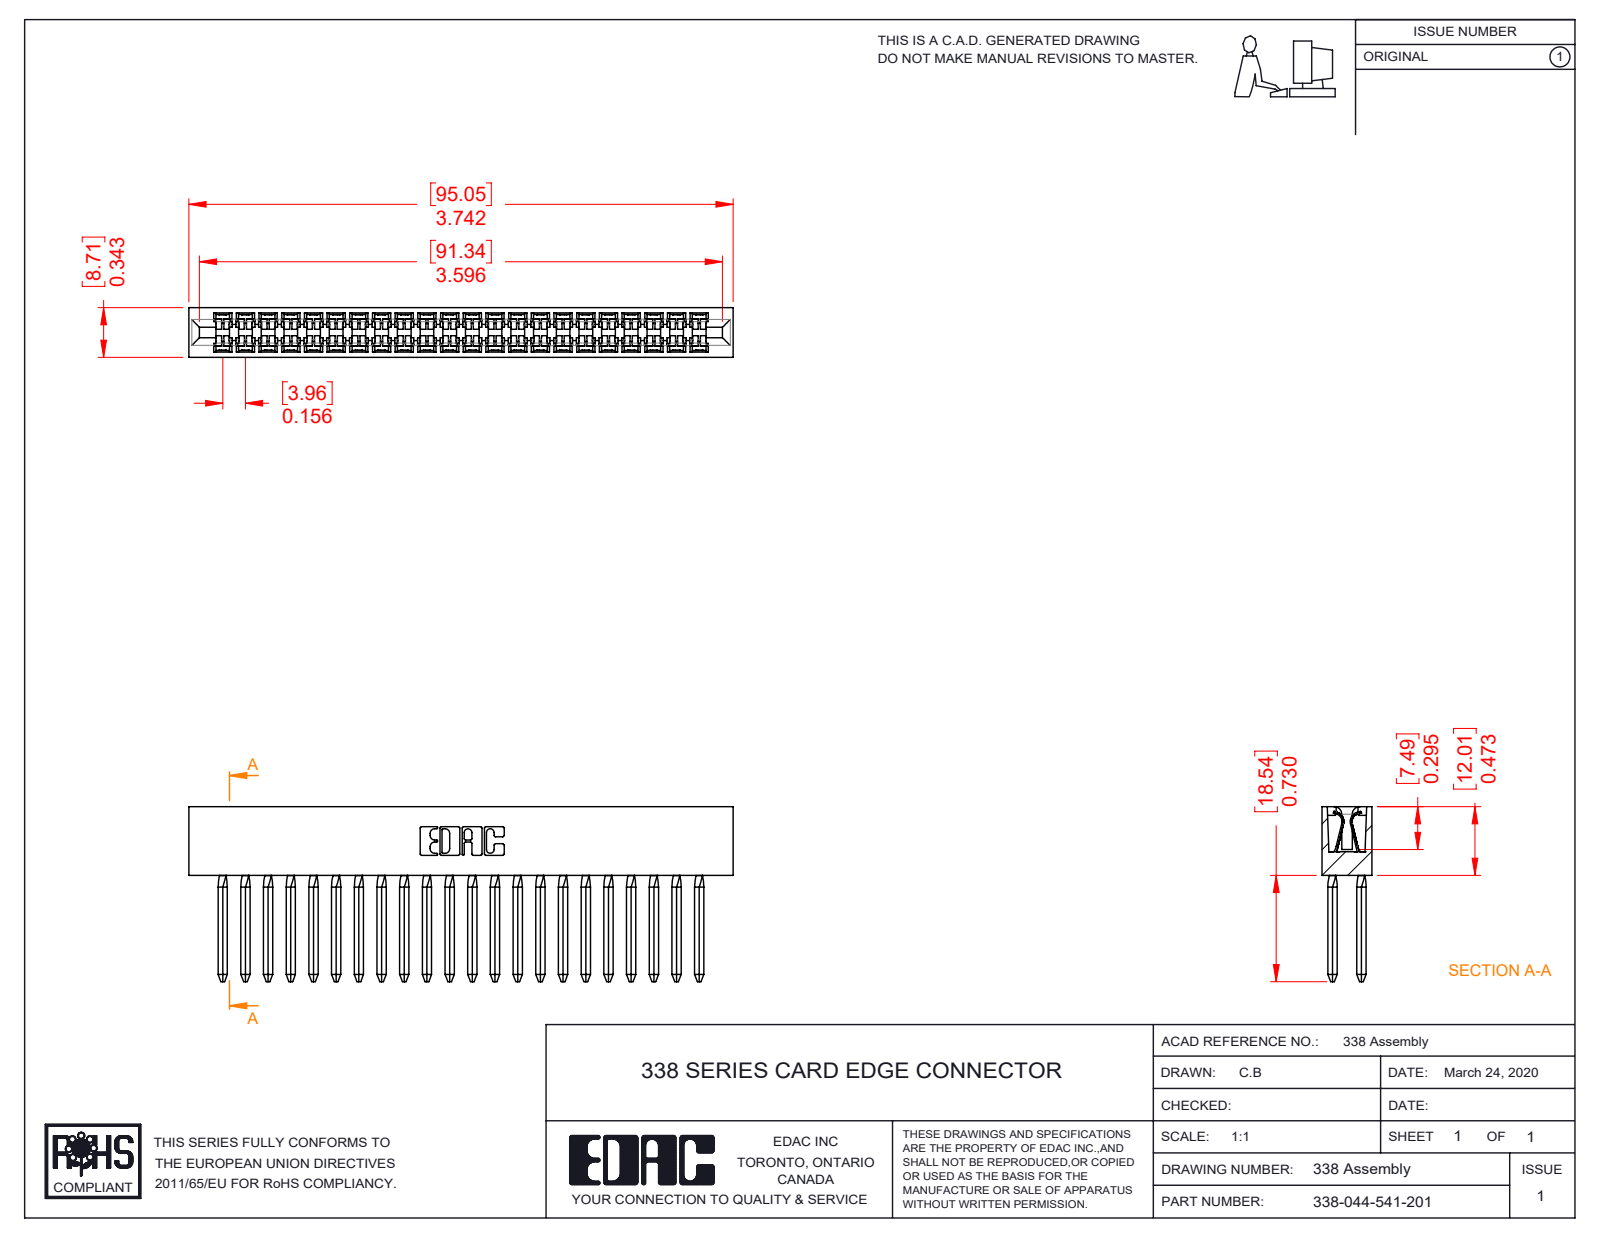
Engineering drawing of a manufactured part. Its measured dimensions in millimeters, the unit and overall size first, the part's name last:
Units: millimetres
Overall size (bounding box): 95 × 30.6 × 8.7
Partial cylindrical surfaces — rounded edges, fillets, slot ends (radius × count): R0.6 ×134, R0.2 ×44, R1.4 ×36, R1.7 ×36, R2.5 ×35, R0.3 ×22, R0.2 ×6, R0.8 ×6
Main face-to-face distances: 8.7, 4, 15.8, 2.8, 19.8, 11.9, 5.3, 3.4, 31.7, 7.9
Volume: 7 700 mm³ · Surface area: 14 780 mm²
Bodies: 45 solids, 3034 faces (2114 planar, 744 cylindrical, 176 other)
Part name (STEP PRODUCT): 338-210-001_338-210-022-001; 338-290-001_541; 338-044-541-201
STEP written by: SolidWorks 2016 (CONFIG_CONTROL_DESIGN)
